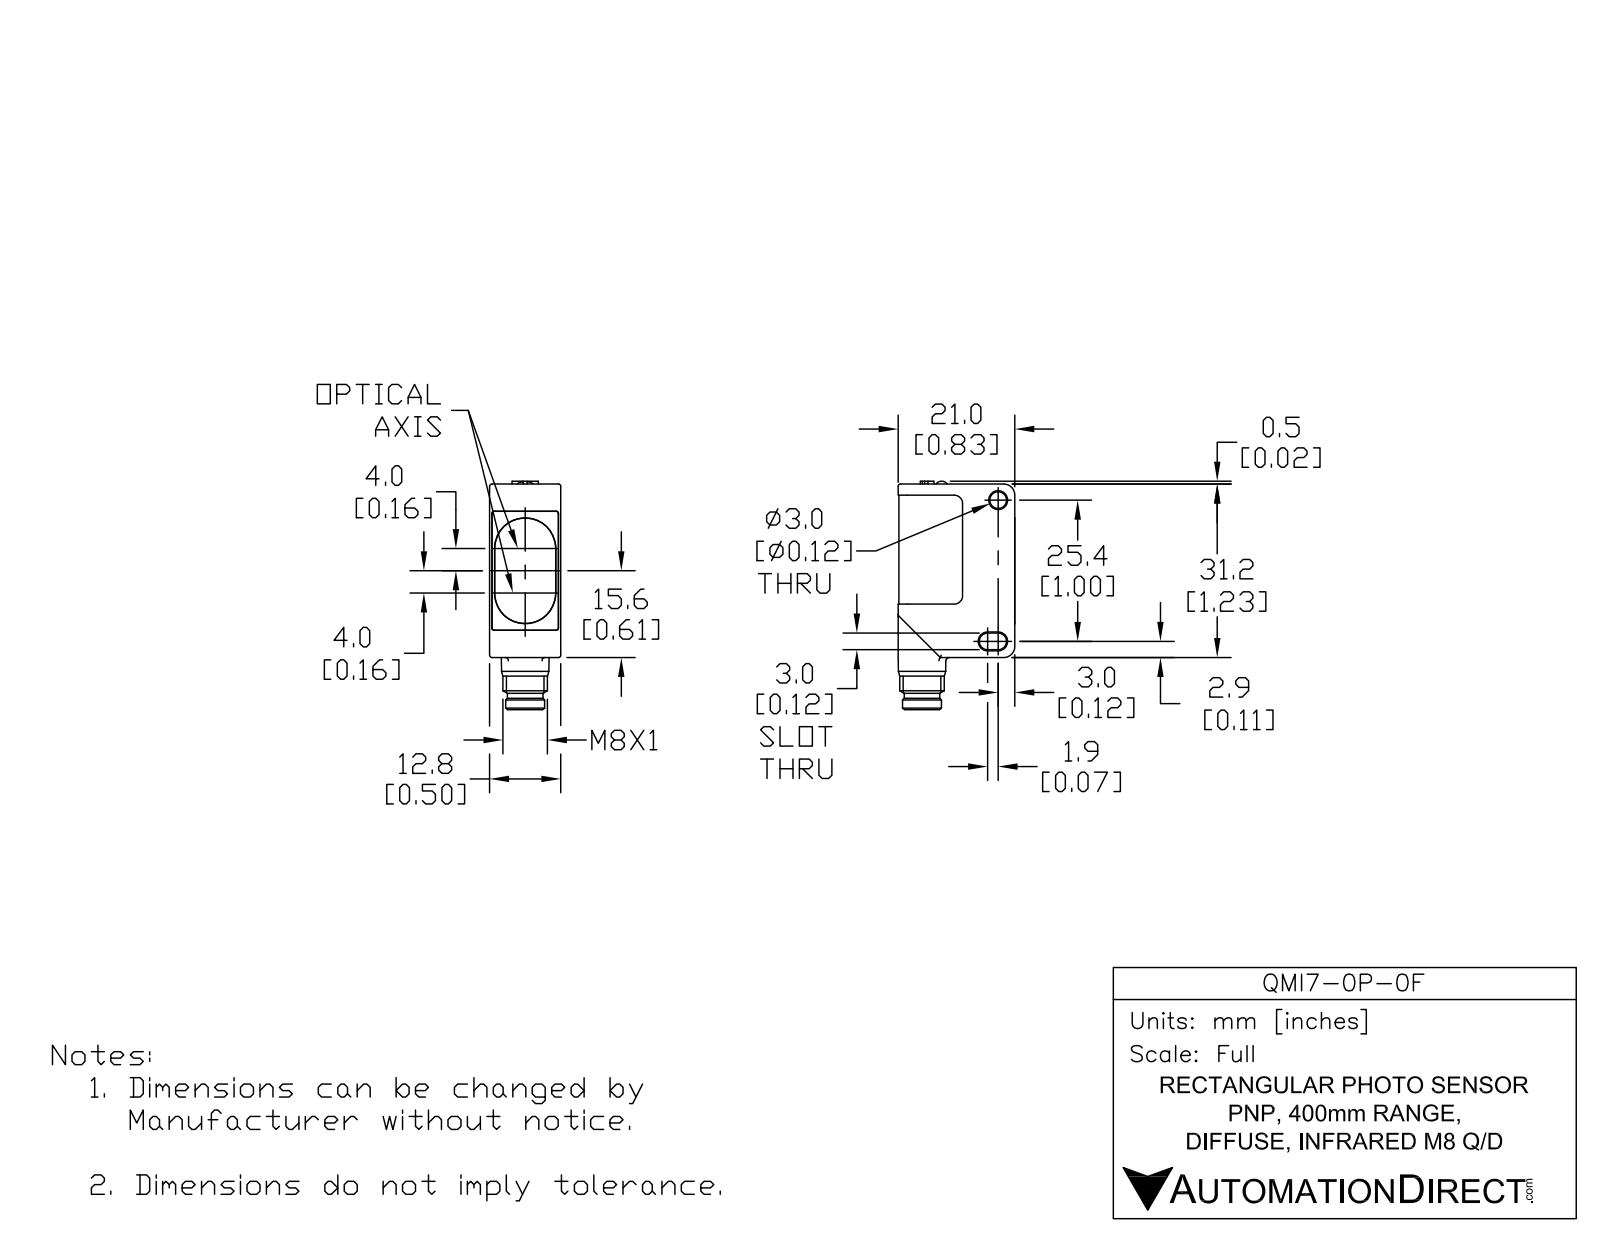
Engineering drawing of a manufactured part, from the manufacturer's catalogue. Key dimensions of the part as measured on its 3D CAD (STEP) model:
Part name (STEP PRODUCT): QMI7-0P-0F
STEP written by: SolidWorks 2017 (AUTOMOTIVE_DESIGN)
Units: inches
Bodies: 7 solids, 272 faces (125 planar, 100 cylindrical, 47 other)
Overall size (bounding box): 1.619 × 0.827 × 0.504
Volume: 0.474 in³ · Surface area: 7.749 in²
Round holes (diameter × count): ⌀0.118 ×3, ⌀0.228 ×1
Round bosses / shafts (diameter × count): ⌀0.039 ×4, ⌀0.138 ×2, ⌀0.315 ×1, ⌀0.276 ×1, ⌀0.252 ×1
Partial cylindrical surfaces — rounded edges, fillets, slot ends (radius × count): R0.016 ×10, R0.02 ×9, R0.059 ×6, R0.024 ×4, R0.039 ×4, R0.006 ×2, R0.044 ×2, R0.065 ×2
Main face-to-face distances: 0.498, 0.02, 0.504, 0.11, 0.016, 0.492, 0.488, 0.482, 0.059, 0.711
Hole centre spacings: 0.04, 0.205, 0.245
